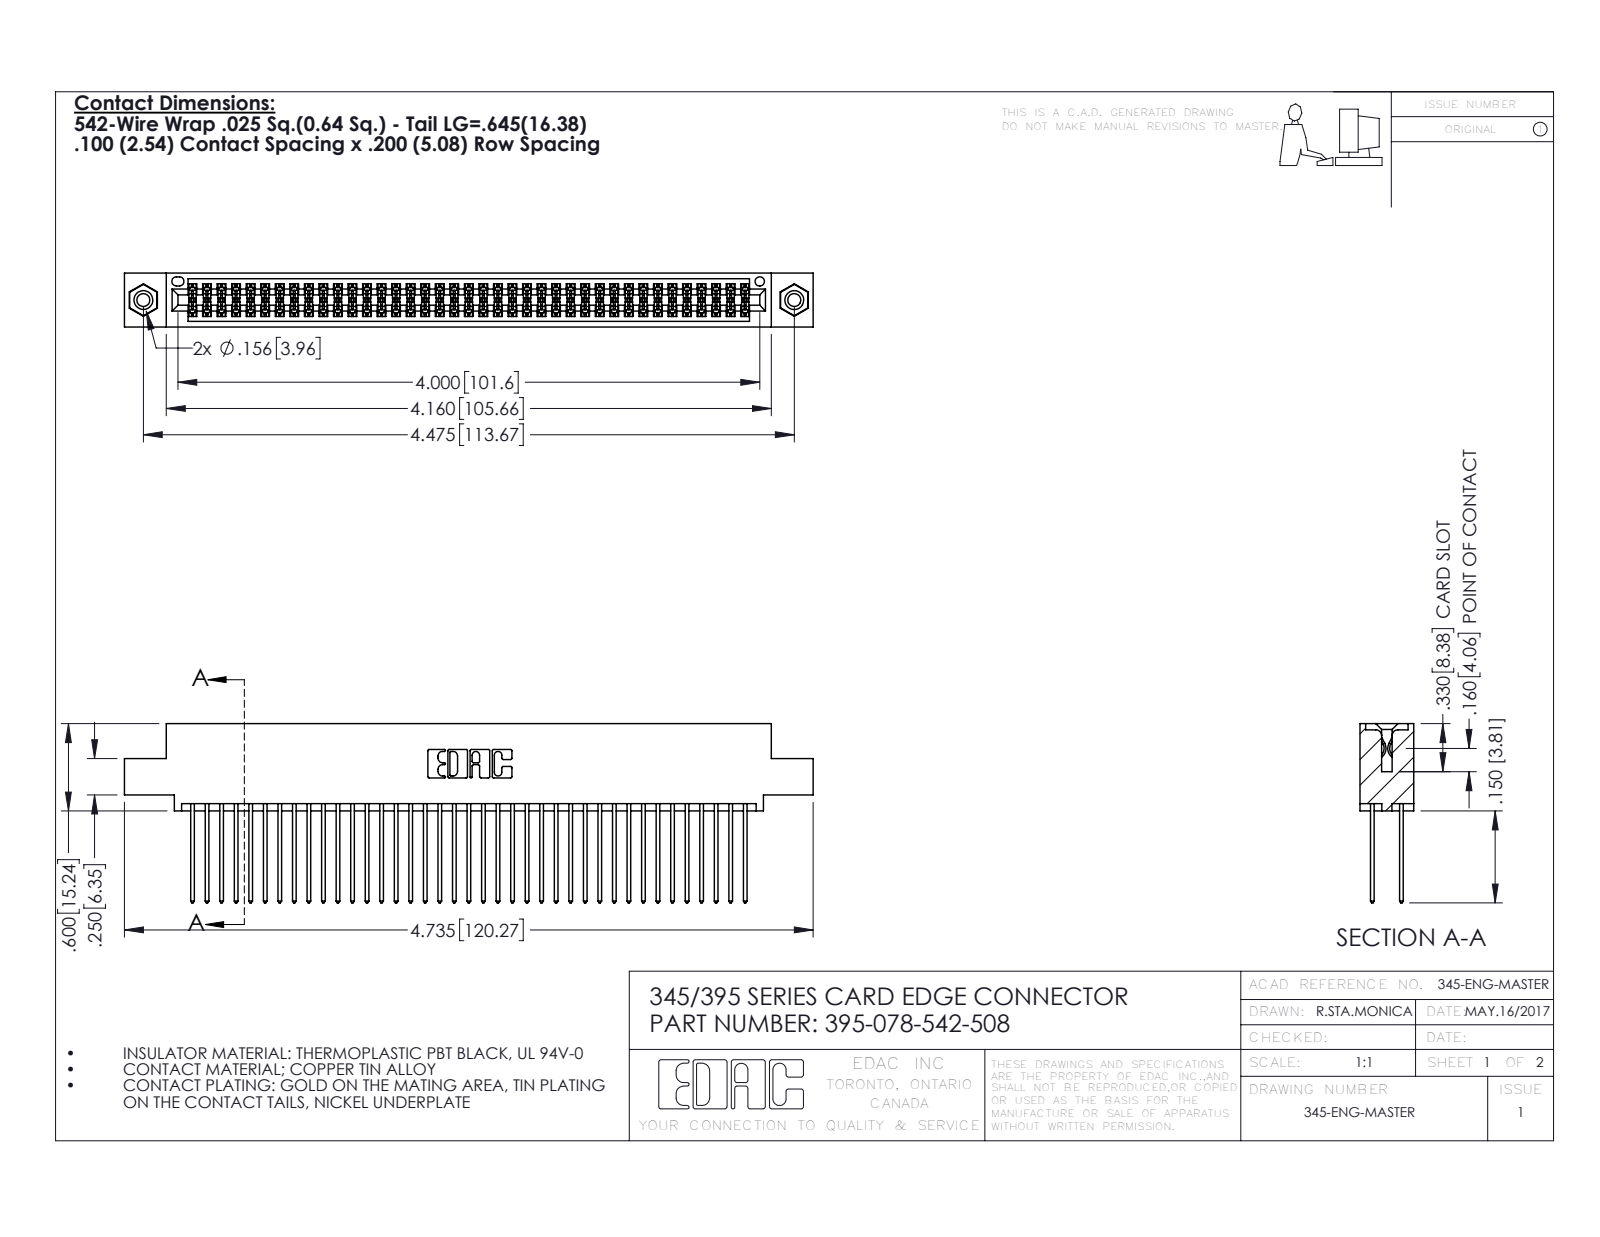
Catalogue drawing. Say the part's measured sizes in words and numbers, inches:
The part is named "345-250-001_345-250-003-102; 345 Part_0.110 Offset - 0.156 Dia-TI; 345-292-001_345-293-142; 395-078-542-508". Its 3-D file was written by "SolidWorks 2016 (CONFIG_CONTROL_DESIGN)". It is 81 solids with 4090 faces: 2690 planar, 1384 cylindrical and 16 other. Overall it measures 4.735 by 1.232 by 0.37 inches. Its volume is 0.729 cubic inches and its surface area 30.06 square inches. Round holes: 2 of diameter 0.089, 2 of diameter 0.125, 2 of diameter 0.156, 1 of diameter 0.064. Round bosses or shafts: 2 of diameter 0.155. Partial cylindrical surfaces (rounded edges, fillets, slot ends): 117 of radius 0.006, 78 of radius 0.01, 22 of radius 0.01, 6 of radius 0.007, 6 of radius 0.031, 3 of radius 0.026, 2 of radius 0.014, 2 of radius 0.019. The main face-to-face distances are 0.072, 0.298, 0.2, 0.098, 0.272, 0.025, 0.225, 0.37, 0.175, 0.149. The hole center spacings are 0.27, 4.239, 4.475.
